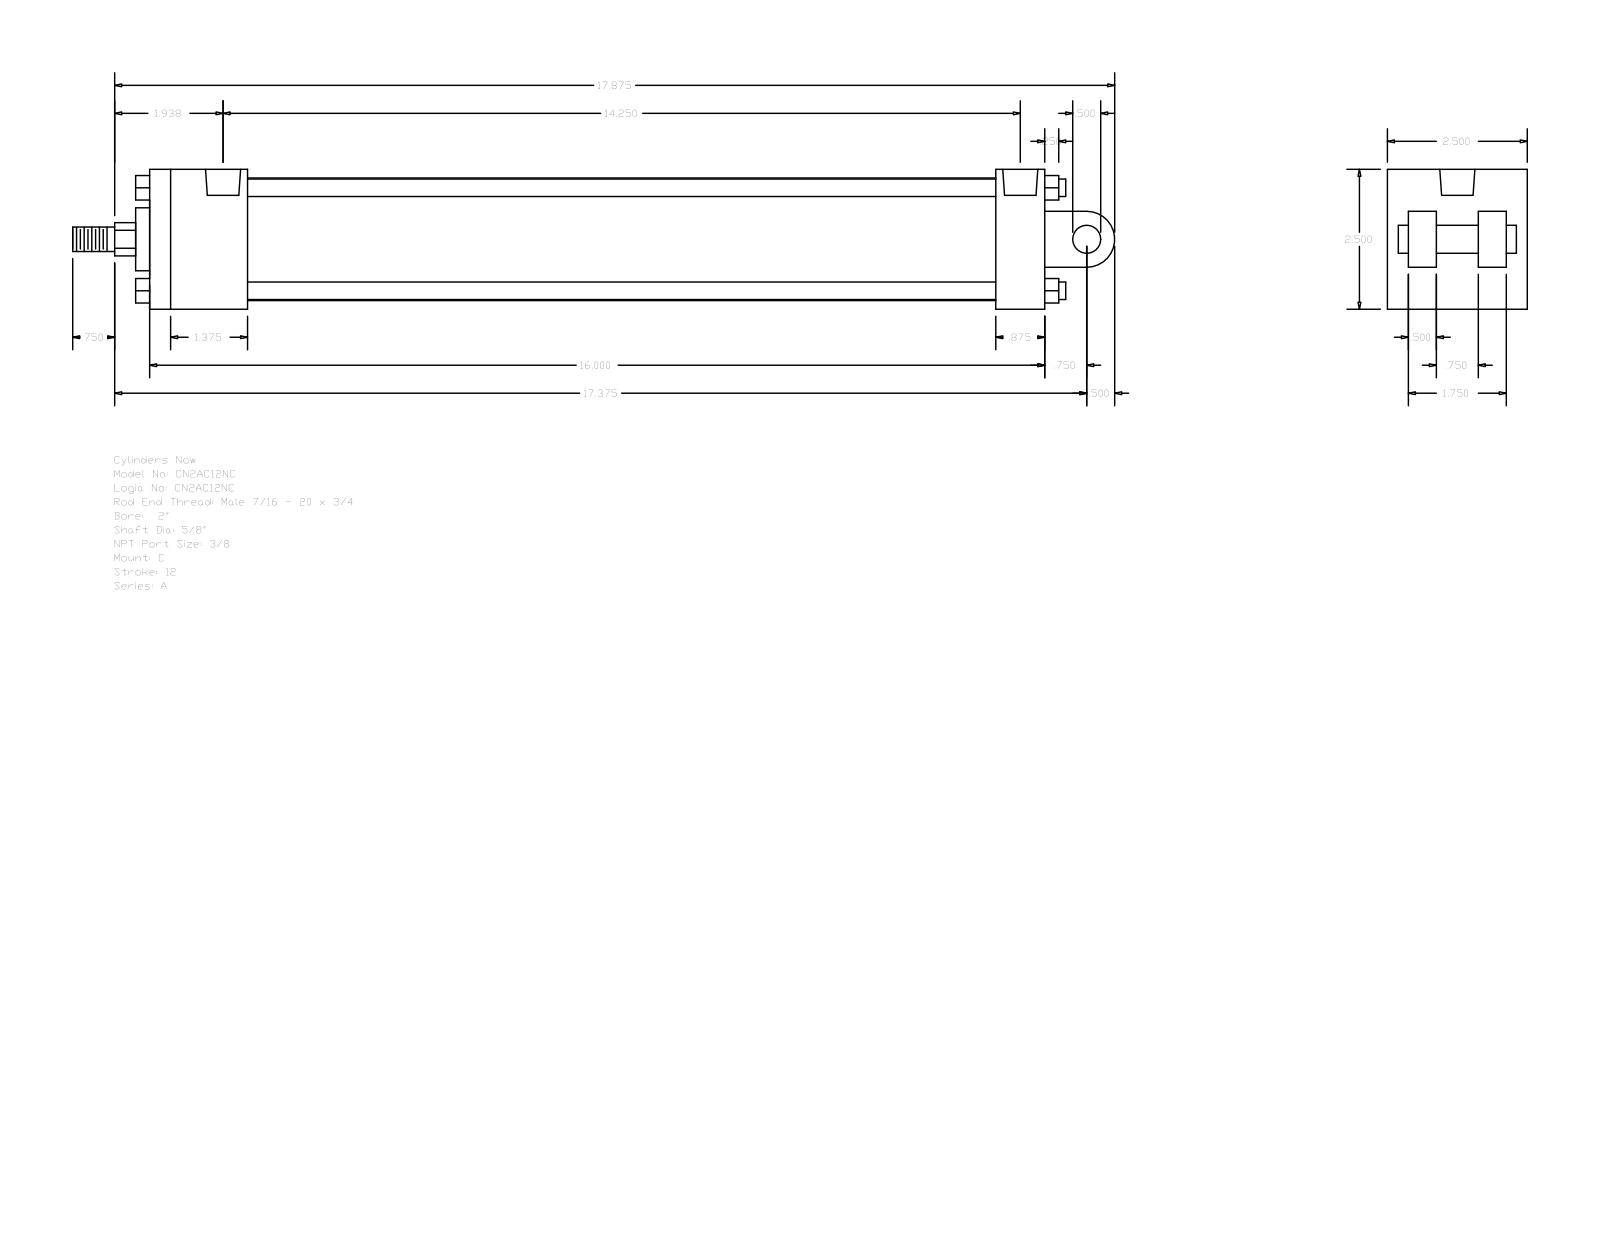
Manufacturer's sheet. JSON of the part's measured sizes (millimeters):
{"part_name": "A_C__0200_0.625", "step_written_by": "GSSL Pune (CONFIG_CONTROL_DESIGN)", "units": "millimeters", "bodies": {"solids": 0, "faces": 135, "planar": 102, "cylindrical": 33, "other": 0}, "overall_size": [473.07, 63.5, 63.5], "round_holes": [[5.56, 4], [15.93, 2]], "round_bosses_or_shafts": [[7.94, 4], [55.63, 1], [28.57, 1], [15.88, 1], [12.7, 1], [11.11, 1]], "partial_cylinders_radius": [[7.54, 1], [12.7, 1]], "face_to_face_distances": [63.5, 406.39, 22.22, 44.45, 361.94, 384.17, 339.72, 12.7, 6.35, 53.98], "hole_center_spacings": [354, 3.97, 3.98, 357.97, 357.98, 361.95]}
